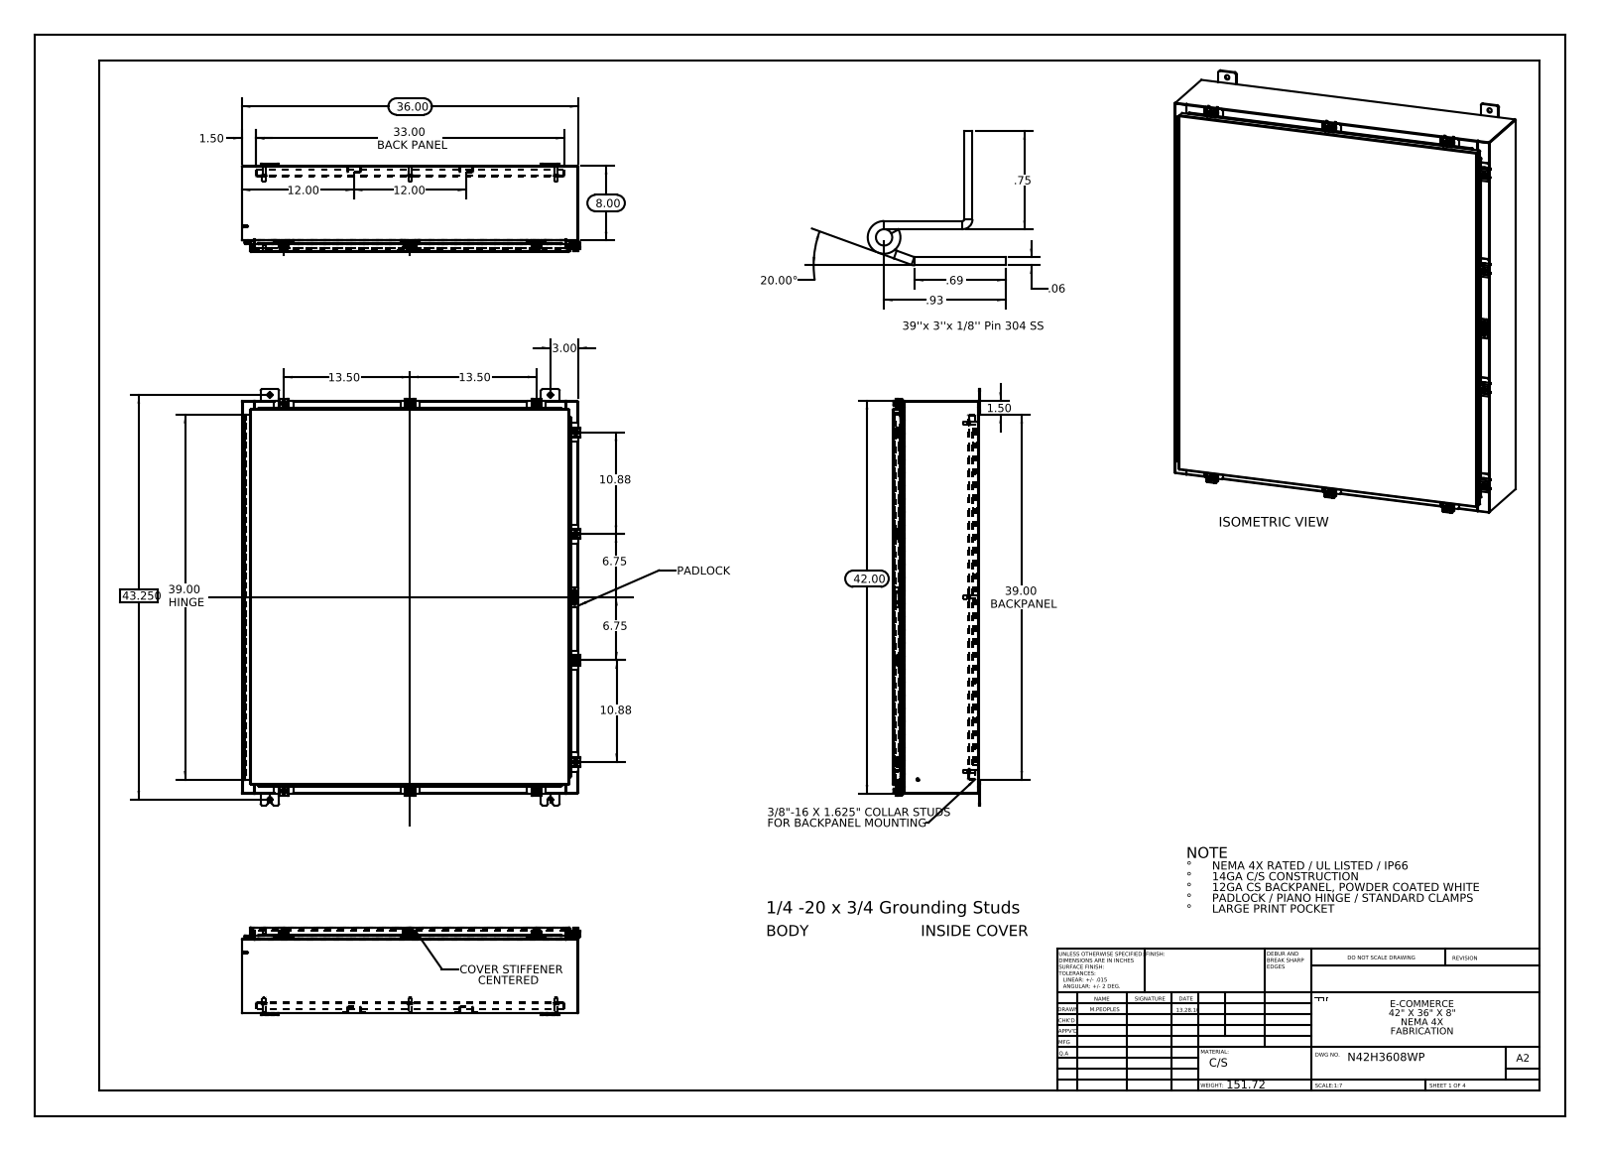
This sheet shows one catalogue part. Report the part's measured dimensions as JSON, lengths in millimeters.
{"part_name": "N42H3608SSWP Backpanel; 10_30 CD Stud; N42H3608SSWP 22101002; N42H3608SSWP Clamp Top (+8 more)", "step_written_by": "SolidWorks 2013 (CONFIG_CONTROL_DESIGN)", "units": "millimeters", "bodies": {"solids": 82, "faces": 2971, "planar": 1514, "cylindrical": 1229, "other": 228}, "overall_size": [1130.3, 919.8, 238.5], "volume_mm3": 8720000, "surface_area_mm2": 8533000, "round_holes": [[12.7, 12], [5.4, 10], [6.6, 10], [6.4, 6], [3.2, 2]], "round_bosses_or_shafts": [[6.4, 11], [12.7, 10], [10.1, 10], [15.9, 8], [9.5, 8], [8.4, 8], [4, 6], [3.6, 6]], "partial_cylinders_radius": [[1.5, 46], [0.3, 39], [2.2, 33], [4.8, 24], [3, 20], [3.6, 20], [1.3, 15], [2, 14]], "face_to_face_distances": [1.9, 231.8, 229.9, 233.7, 2.6, 25.4, 206.4, 27.3, 204.5, 29.9], "hole_center_spacings": [342.9, 347, 431.8, 435.5, 473.1, 529.2, 617.5, 659.3]}
